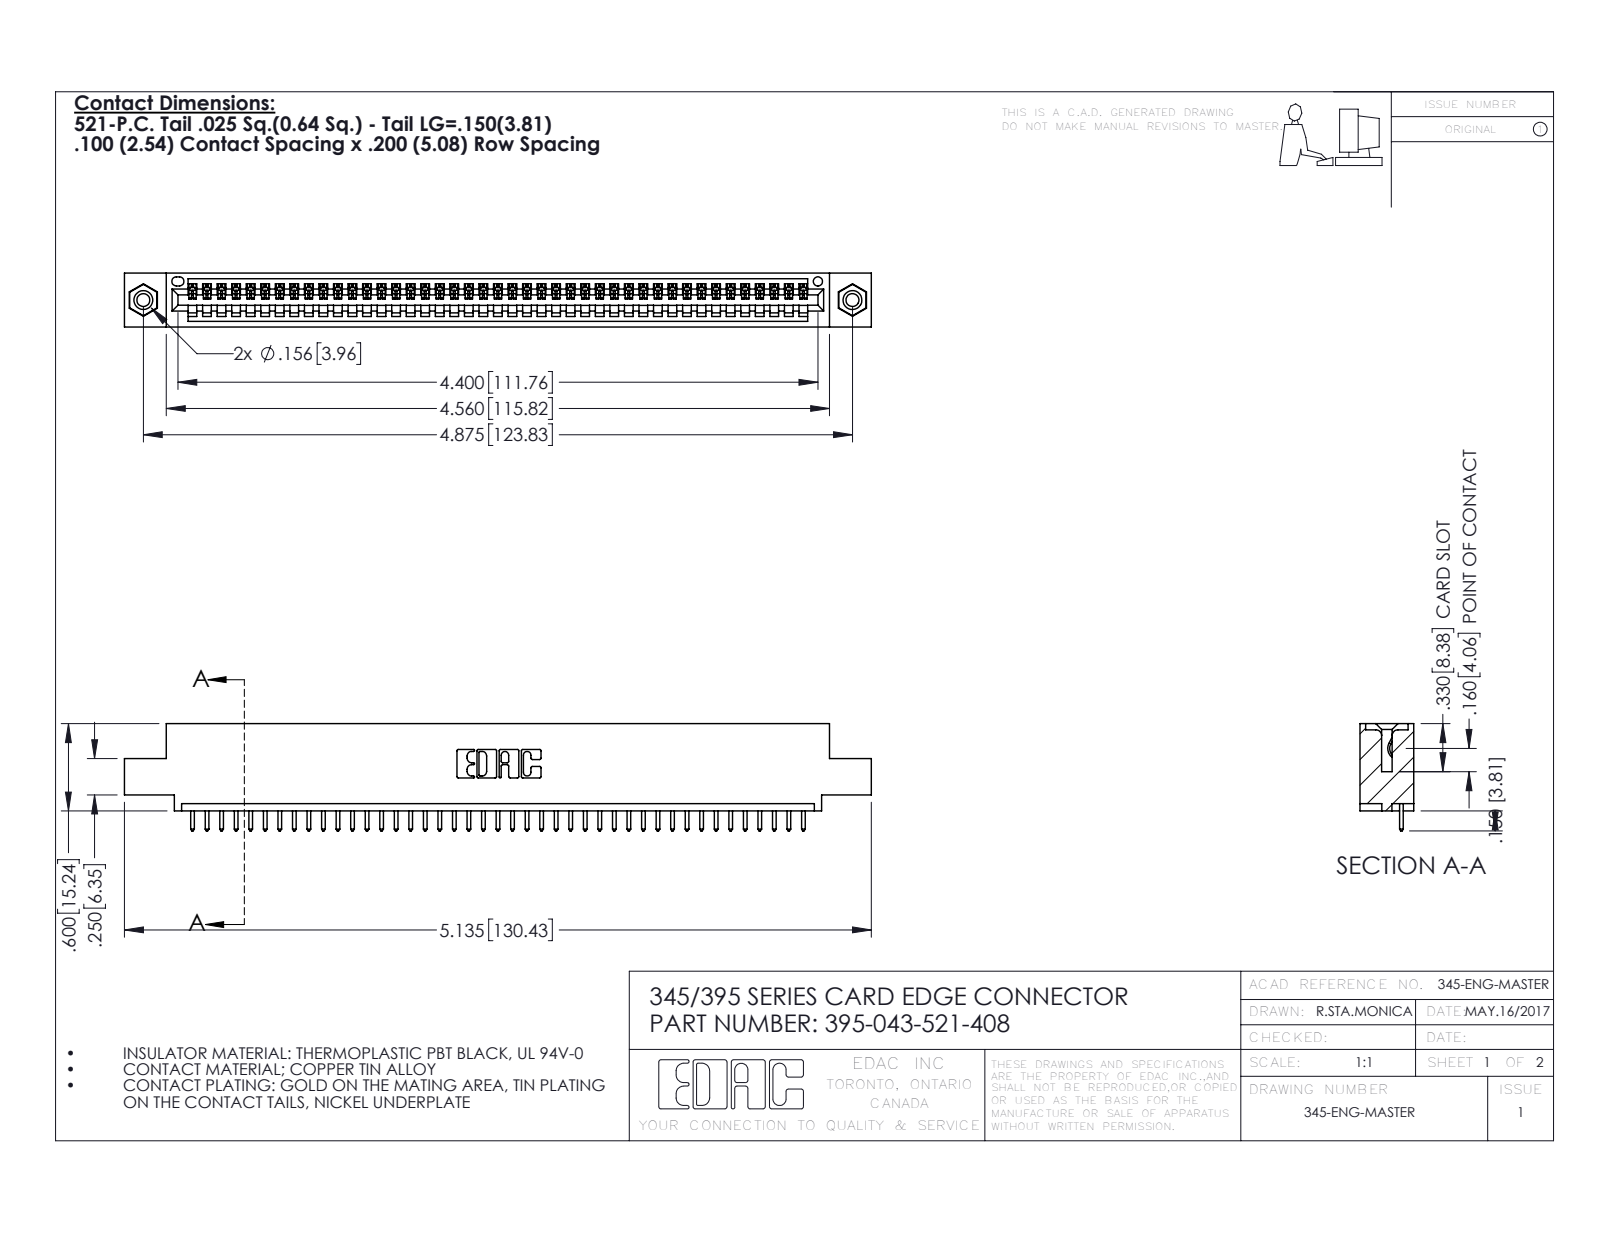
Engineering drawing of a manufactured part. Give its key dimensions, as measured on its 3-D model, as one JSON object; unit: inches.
{"part_name": "395-043-521-408; 345-250-001_345-250-003-102; 345-292-001_345-293-121; 345 Part_0.110 Offset - 0.156 Dia-TI", "step_written_by": "SolidWorks 2016 (CONFIG_CONTROL_DESIGN)", "units": "inches", "bodies": {"solids": 46, "faces": 2684, "planar": 1836, "cylindrical": 832, "other": 16}, "overall_size": [5.135, 0.737, 0.37], "volume_in3": 0.744, "surface_area_in2": 24.55, "round_holes": [[0.089, 2], [0.125, 2], [0.156, 2], [0.064, 1]], "round_bosses_or_shafts": [[0.155, 2]], "partial_cylinders_radius": [[0.006, 86], [0.01, 86], [0.01, 22], [0.007, 6], [0.031, 6], [0.026, 3], [0.031, 2], [0.04, 2]], "face_to_face_distances": [0.072, 0.298, 0.37, 0.2, 0.098, 0.272, 0.025, 0.225, 0.149, 0.072], "hole_center_spacings": [0.27, 4.639, 4.875]}
